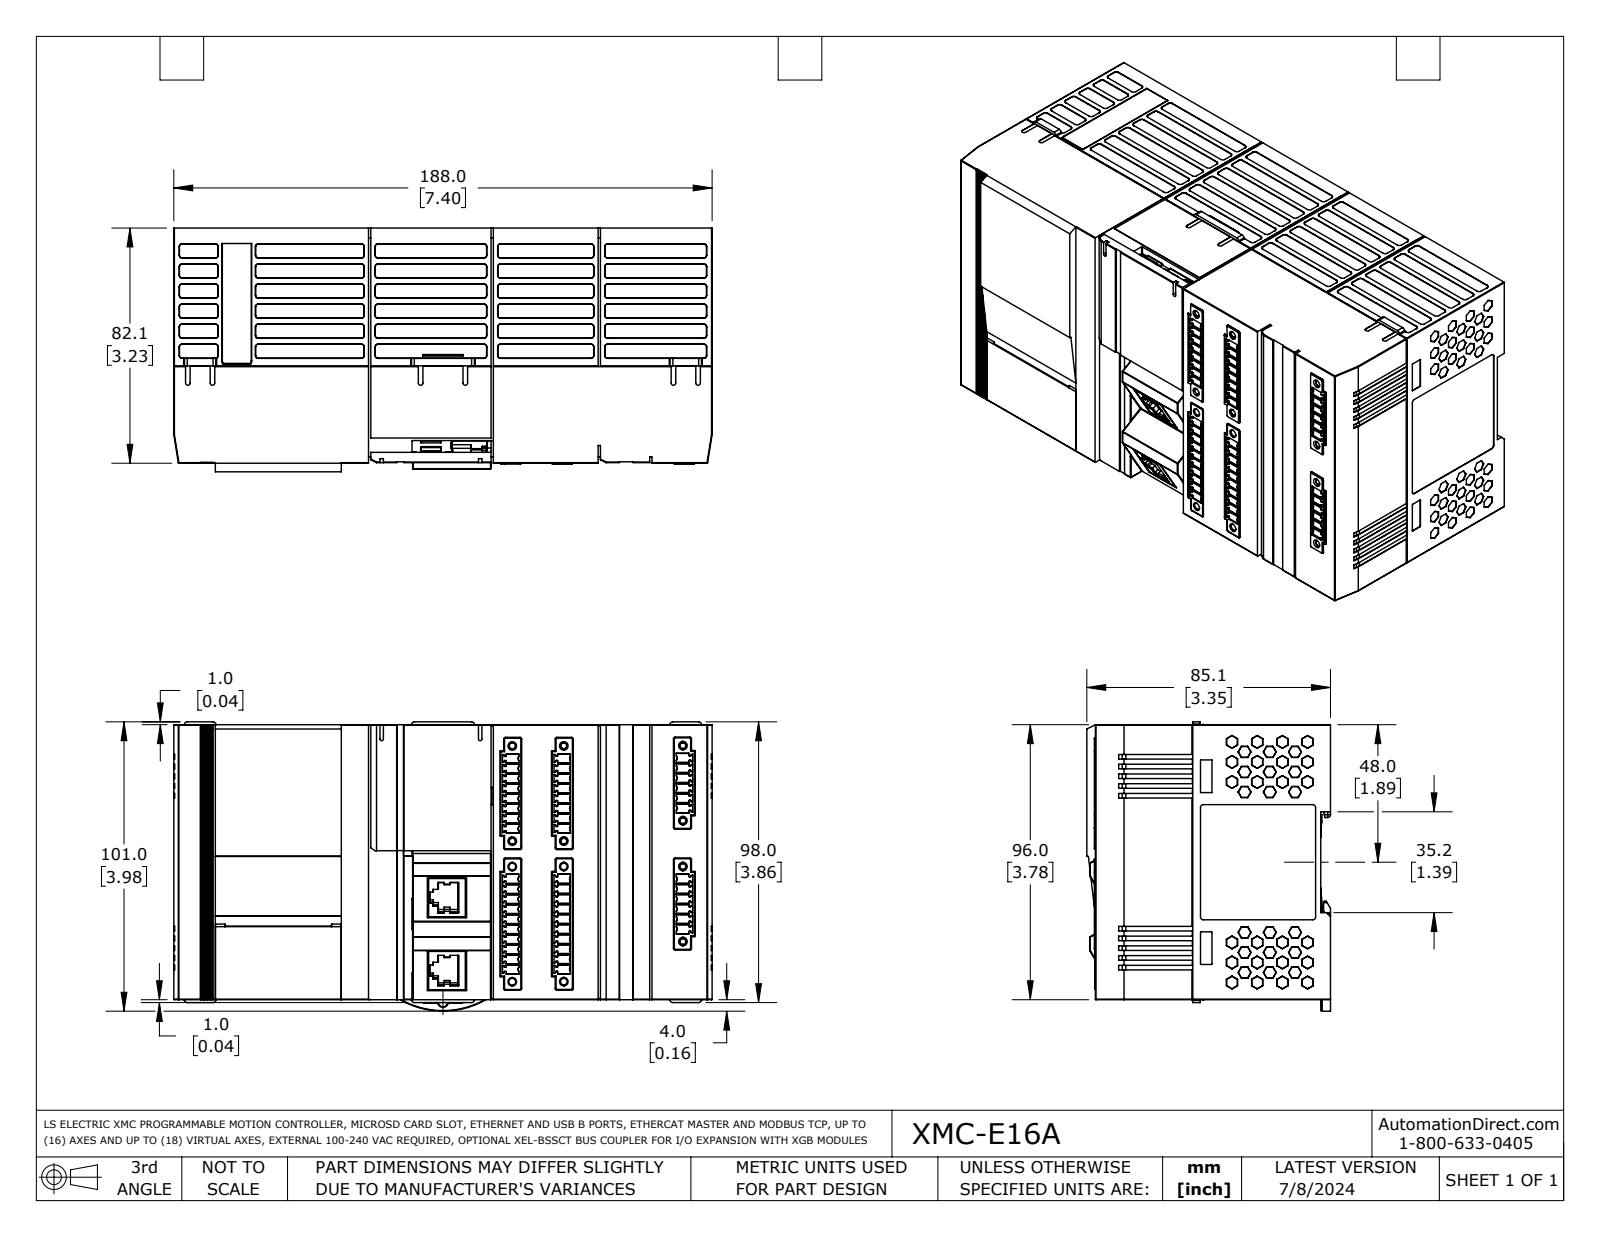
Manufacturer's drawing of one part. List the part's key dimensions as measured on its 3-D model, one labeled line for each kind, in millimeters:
Part name (STEP PRODUCT): XMC-E16A
STEP written by: SolidWorks 2021 (AUTOMOTIVE_DESIGN)
Units: millimetres
Bodies: 1 solid, 4897 faces (3156 planar, 1086 cylindrical, 655 other)
Overall size (bounding box): 188 × 101 × 85.1
Volume: 1 427 000 mm³ · Surface area: 101 200 mm²
Round holes (diameter × count): ⌀2 ×4, ⌀2.1 ×1, ⌀2.5 ×1, ⌀3.4 ×1
Round bosses / shafts (diameter × count): ⌀5.3 ×5, ⌀3 ×5, ⌀2 ×4, ⌀5.2 ×1, ⌀4 ×1
Partial cylindrical surfaces — rounded edges, fillets, slot ends (radius × count): R0.2 ×448, R0.5 ×144, R1 ×87, R0.3 ×46, R1.6 ×40, R0.6 ×27, R0.3 ×12, R0.8 ×7
Main face-to-face distances: 95.9, 96, 78.7, 95.9, 187.9, 82.1, 188, 3.4, 78.5, 81.9
Hole centre spacings: 11.8, 16, 26.2, 26.2, 28.1, 42.2, 42.2, 43.2
